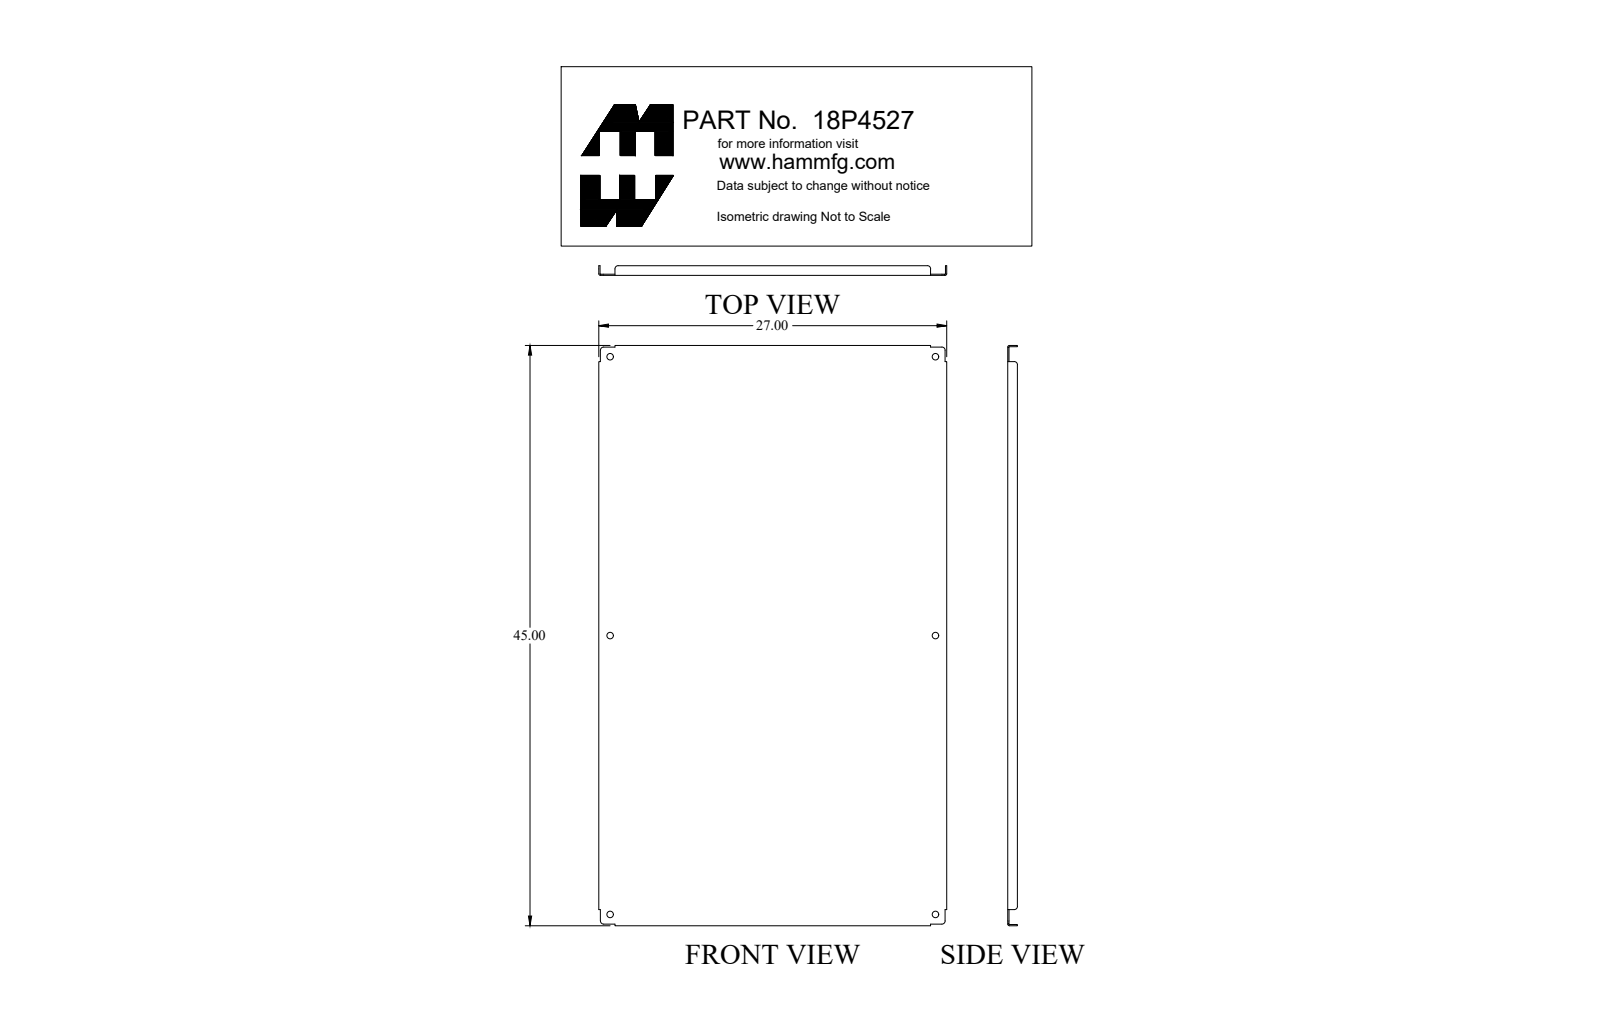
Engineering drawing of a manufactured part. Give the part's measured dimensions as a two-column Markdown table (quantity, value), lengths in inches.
| quantity | value |
| --- | --- |
| part name | 18P4527_Default |
| STEP written by | SolidWorks 2018 (CONFIG_CONTROL_DESIGN) |
| units | inches |
| bodies | 1 solid, 62 faces (30 planar, 32 cylindrical, 0 other) |
| overall size | 45 × 27 × 0.75 |
| volume | 123.1 in³ |
| surface area | 2 606 in² |
| round holes (diameter × count) | 0.5 × 6 |
| partial cylindrical surfaces (radius × count) | 0.25 × 8, 0.03 × 4, 0.125 × 4 |
| main face-to-face distances | 0.095, 26.905, 44.905, 27, 26.81, 45, 44.81, 0.75, 0.655, 0.125 |
| hole center spacings | 21.625, 33.245, 25.25, 43.25, 50.081 |
